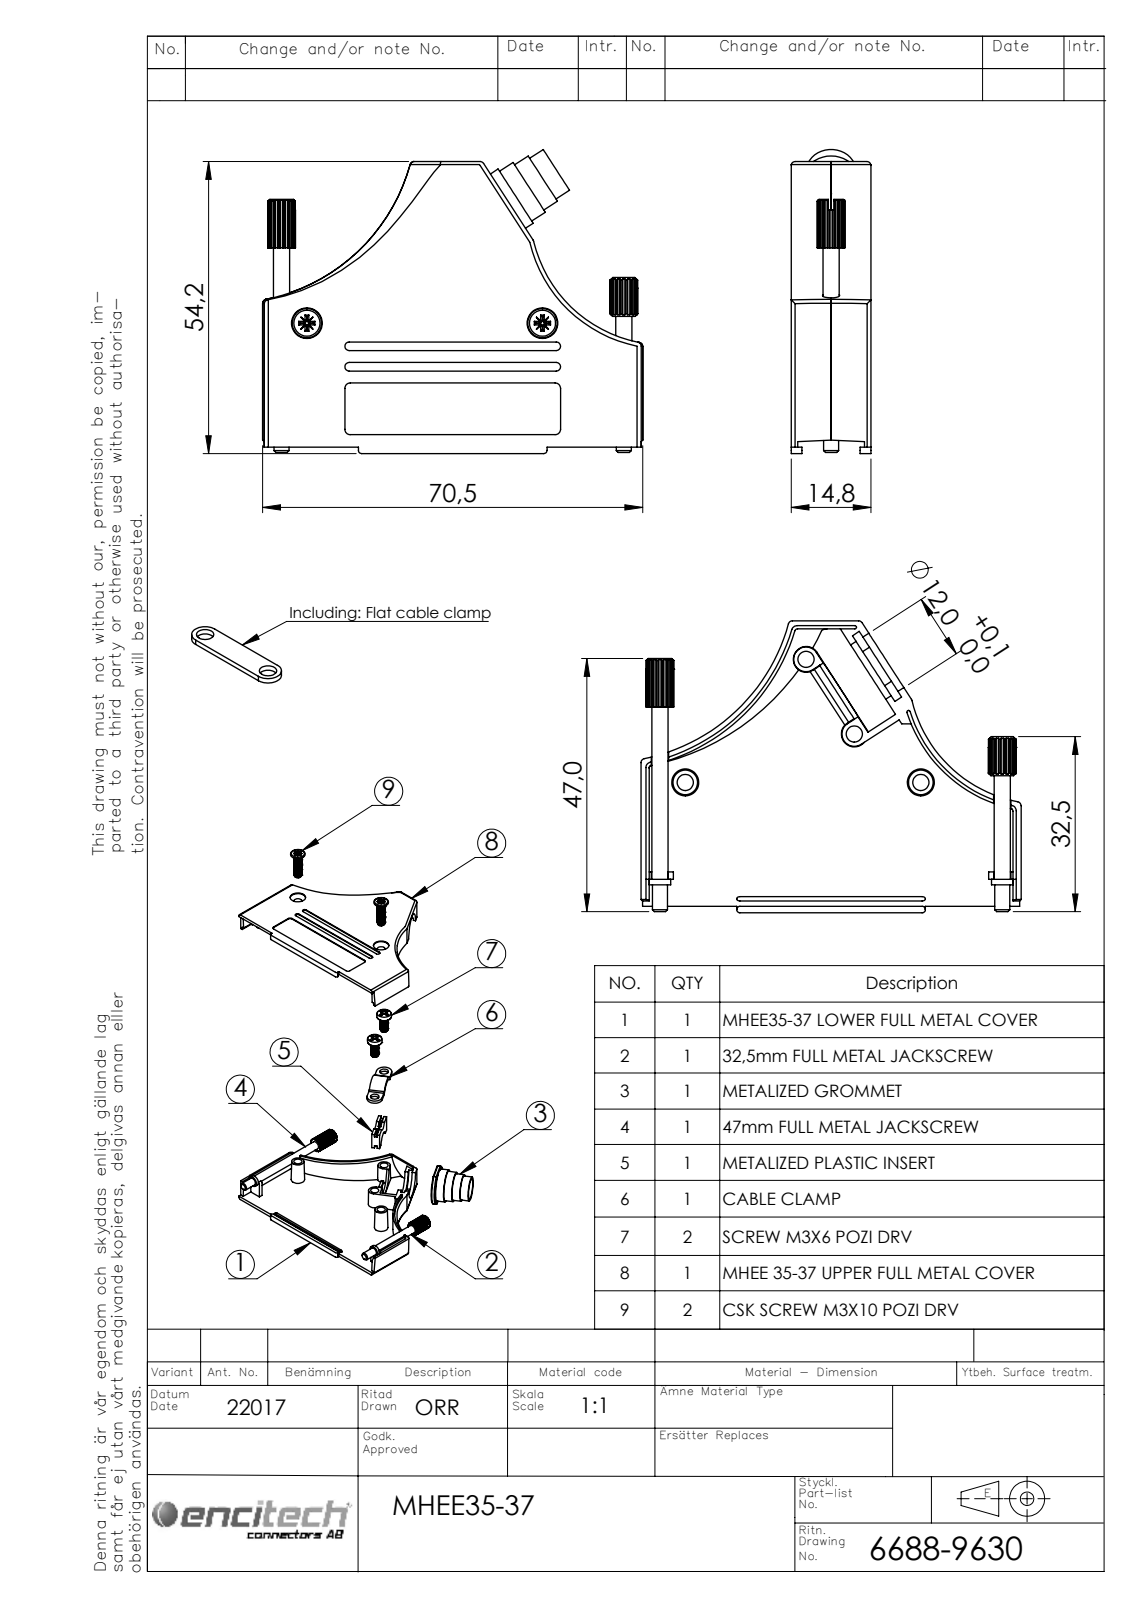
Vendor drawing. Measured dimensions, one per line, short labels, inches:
name: 6805-0139-14; 6855-0117-03; 6826-0141-01; Plastic insert MHEE (+6 more)
written by: SolidWorks 2021 (AUTOMOTIVE_DESIGN)
unit: in
bodies: 11 solids, 845 faces (408 planar, 312 cylindrical, 125 other)
size: 2.776 × 2.222 × 0.583
volume: 0.671 in³; area: 29.96 in²
holes: 4× ⌀0.118, 4× ⌀0.126, 2× ⌀0.191, 2× ⌀0.224, 1× ⌀0.295, 1× ⌀0.335, 1× ⌀0.374, 1× ⌀0.413, 1× ⌀0.472
bosses: 4× ⌀0.114, 2× ⌀0.157, 2× ⌀0.118, 2× ⌀0.11, 1× ⌀0.433, 1× ⌀0.394, 1× ⌀0.354
rounds: 10× R0.03, 9× R0.039, 8× R0.004, 6× R0.012, 4× R0.031, 3× R0.015, 2× R0.02, 2× R0.024
face distances: 0.047, 0.535, 0.488, 0.583, 0.571, 0.035, 0.524, 0.244, 0.291, 0.28
hole spacings: 0.601, 0.65, 1.23, 1.26, 1.284, 1.72, 2.5
